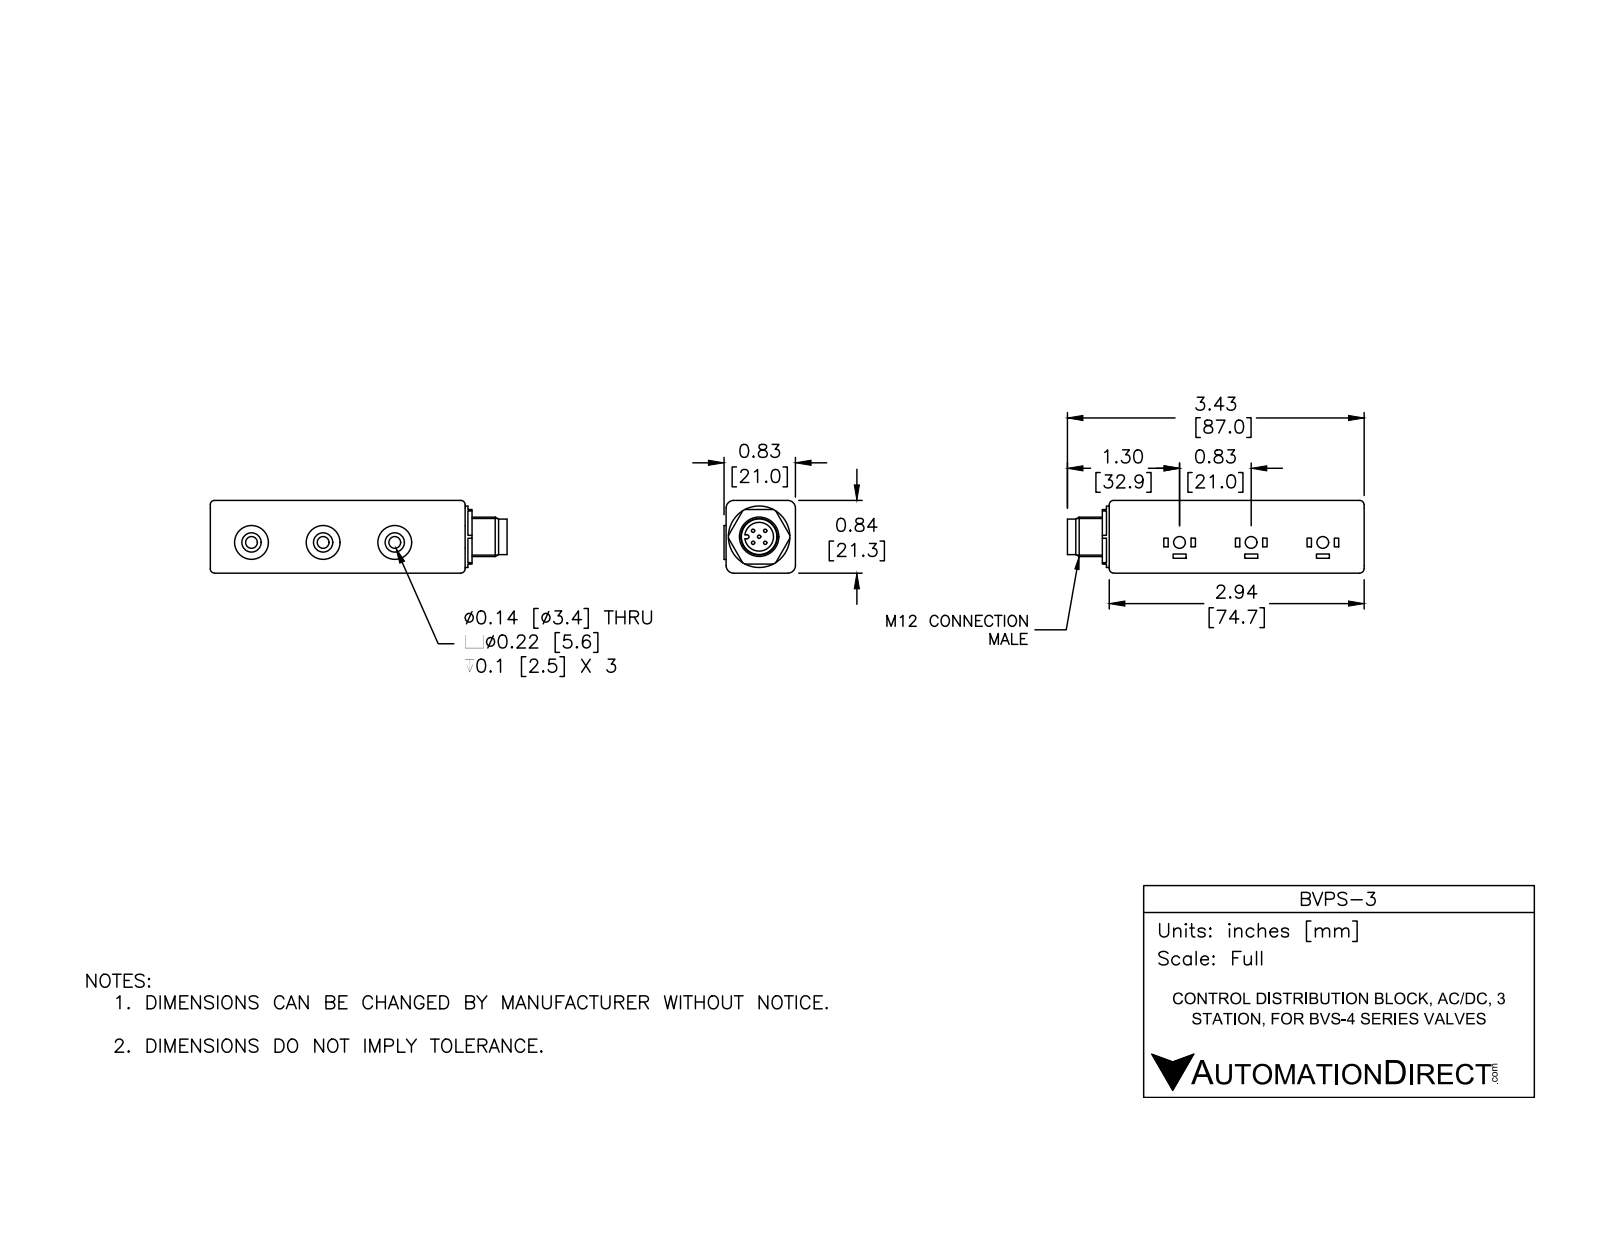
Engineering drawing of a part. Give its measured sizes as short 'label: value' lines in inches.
name: BVPS-3
written by: SolidWorks 2016 (AUTOMOTIVE_DESIGN)
unit: in
bodies: 1 solid, 140 faces (80 planar, 50 cylindrical, 10 other)
size: 3.425 × 0.839 × 0.825
volume: 1.968 in³; area: 13.56 in²
holes: 3× ⌀0.135, 3× ⌀0.222, 1× ⌀0.331
bosses: 5× ⌀0.039, 3× ⌀0.391, 1× ⌀0.709, 1× ⌀0.455, 1× ⌀0.41
rounds: 8× R0.05, 4× R0.087, 1× R0.023
face distances: 0.839, 0.8, 0.05, 0.025, 0.825, 3.022, 0.315, 0.08, 2.942, 0.1
hole spacings: 0.827, 1.654
